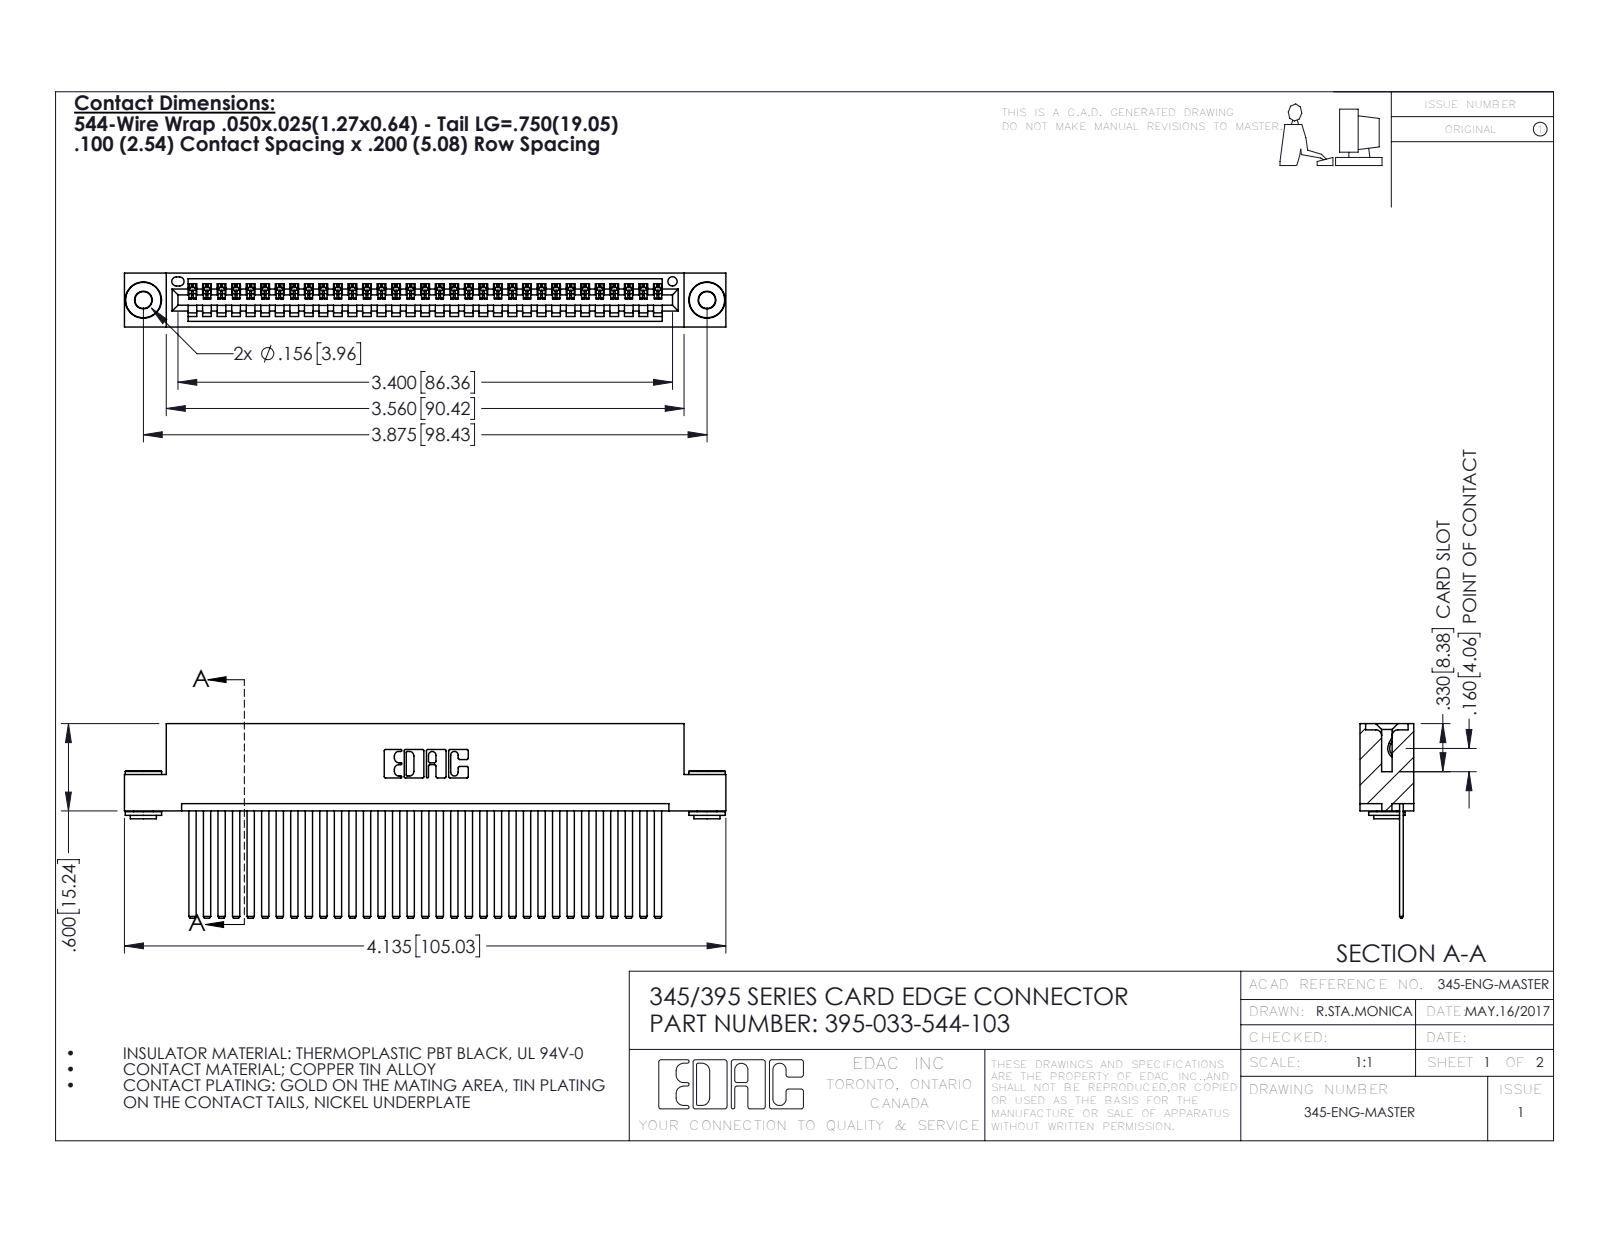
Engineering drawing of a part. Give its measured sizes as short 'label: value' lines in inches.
name: 345-250-002_345-250-002-102; 395-033-544-103; 345-292-001_345-293-144; 345 Part_Flush Mounting Lugs - 0.156 Dia-TH
written by: SolidWorks 2016 (CONFIG_CONTROL_DESIGN)
unit: in
bodies: 36 solids, 1880 faces (1278 planar, 594 cylindrical, 8 other)
size: 4.135 × 1.337 × 0.37
volume: 0.629 in³; area: 23.14 in²
holes: 2× ⌀0.116, 2× ⌀0.156, 1× ⌀0.064
bosses: 2× ⌀0.25, 2× ⌀0.18, 2× ⌀0.136
rounds: 66× R0.006, 22× R0.01, 6× R0.007, 6× R0.031, 3× R0.026, 2× R0.031, 2× R0.04, 1× R0.014
face distances: 0.072, 0.298, 0.025, 0.098, 0.272, 0.2, 0.37, 0.225, 0.149, 0.072
hole spacings: 0.27, 3.64, 3.875
